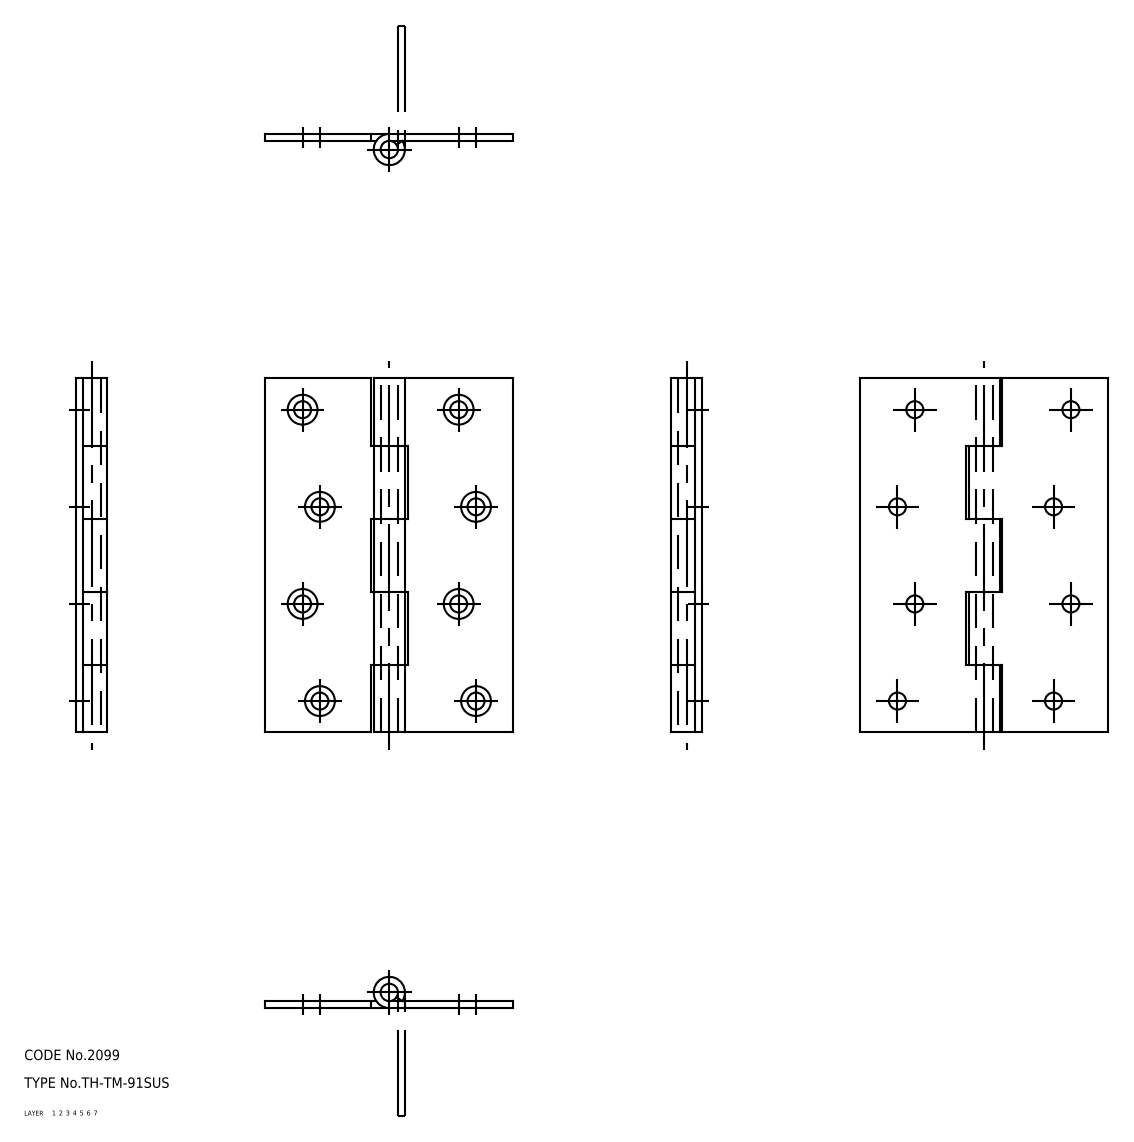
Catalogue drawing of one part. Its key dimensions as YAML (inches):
part_name: "shaft; hinge piece_B; hinge piece_A; TH_TM_91SUS_26934_36"
step_written_by: "CADfix (AUTOMOTIVE_DESIGN)"
units: inches
bodies: {solids: 3, faces: 74, planar: 0, cylindrical: 0, other: 74}
overall_size: [4.016, 2.815, 0.354]
volume: 1.143
surface_area: 31.49
